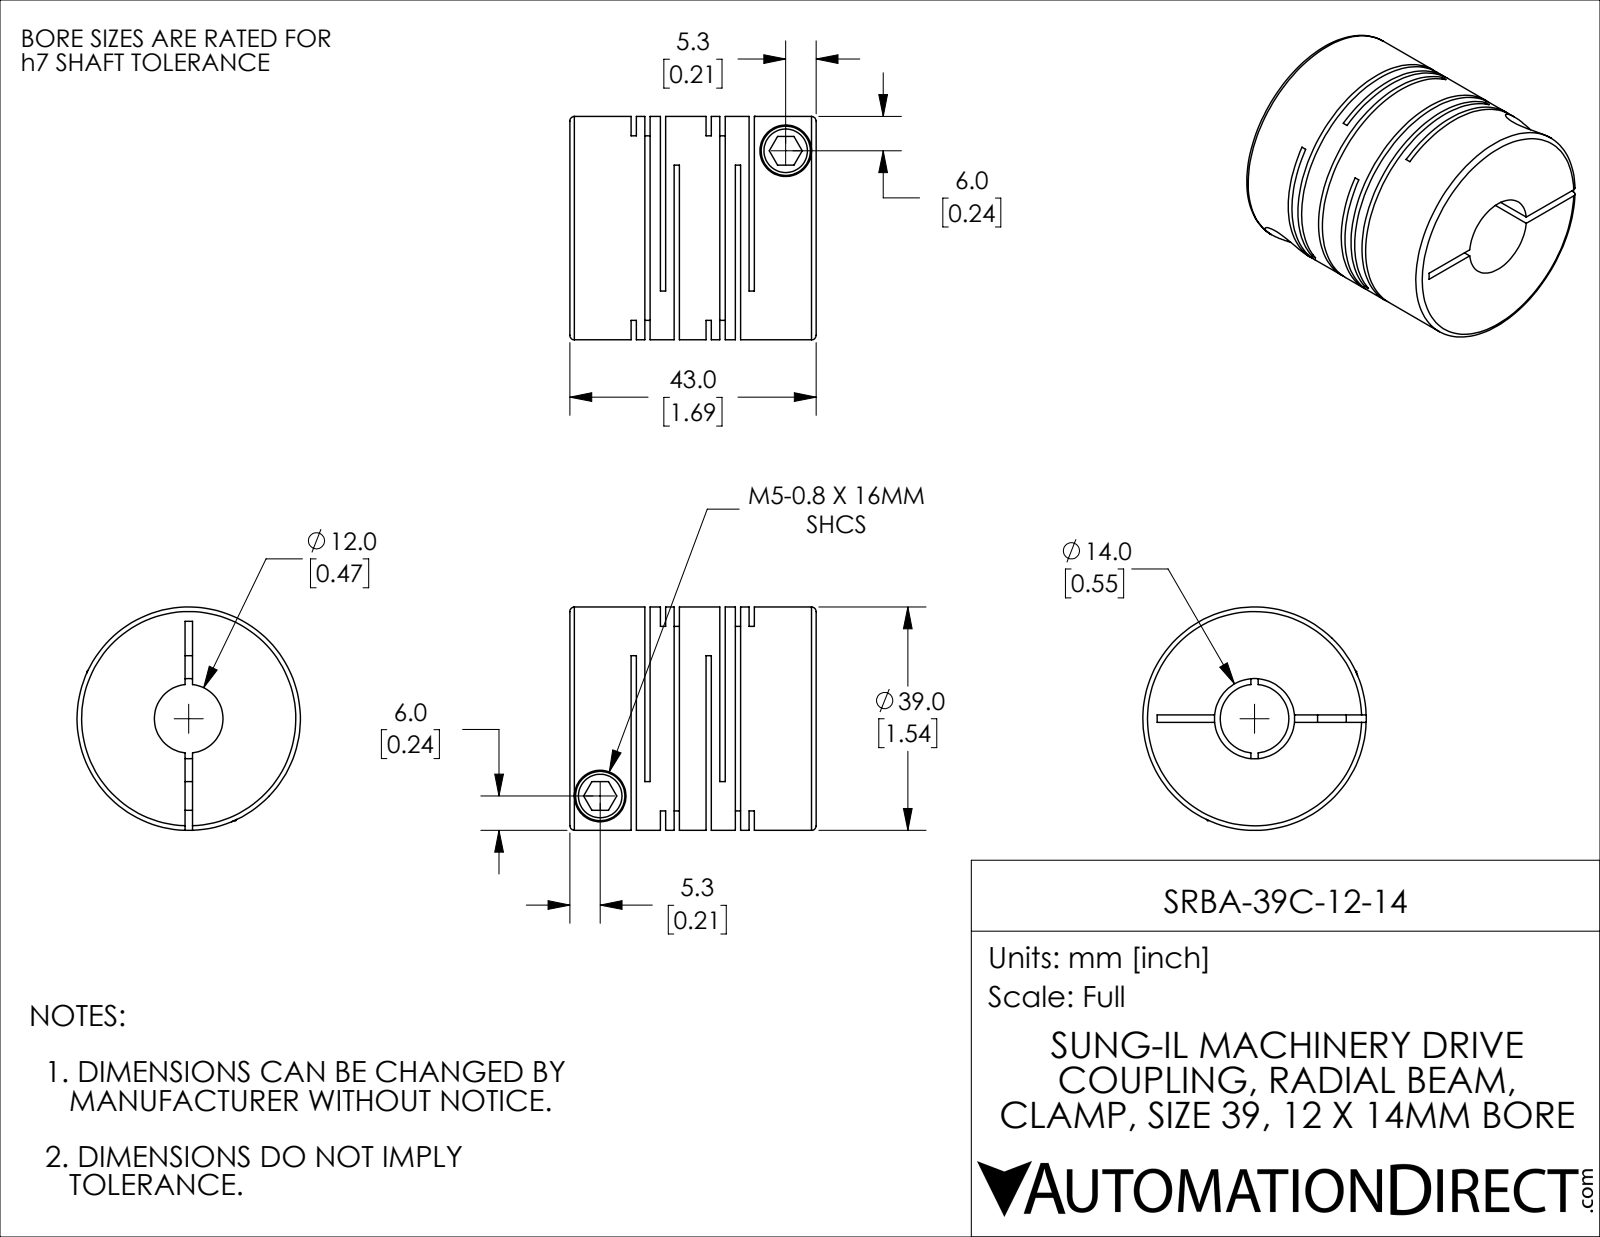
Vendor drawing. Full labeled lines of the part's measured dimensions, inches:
Part name (STEP PRODUCT): SRBA-39C-12-14
STEP written by: SolidWorks 2021 (CONFIG_CONTROL_DESIGN)
Units: inches
Bodies: 1 solid, 114 faces (60 planar, 42 cylindrical, 12 other)
Overall size (bounding box): 1.693 × 1.535 × 1.535
Volume: 2.281 in³ · Surface area: 36.74 in²
Round holes (diameter × count): ⌀0.197 ×2, ⌀0.354 ×2, ⌀0.472 ×1, ⌀0.551 ×1
Round bosses / shafts (diameter × count): ⌀0.339 ×2, ⌀1.535 ×1
Main face-to-face distances: 0.516, 0.036, 0.094, 0.201, 0.421, 0.552, 0.717, 0.131, 0.61, 0.058
